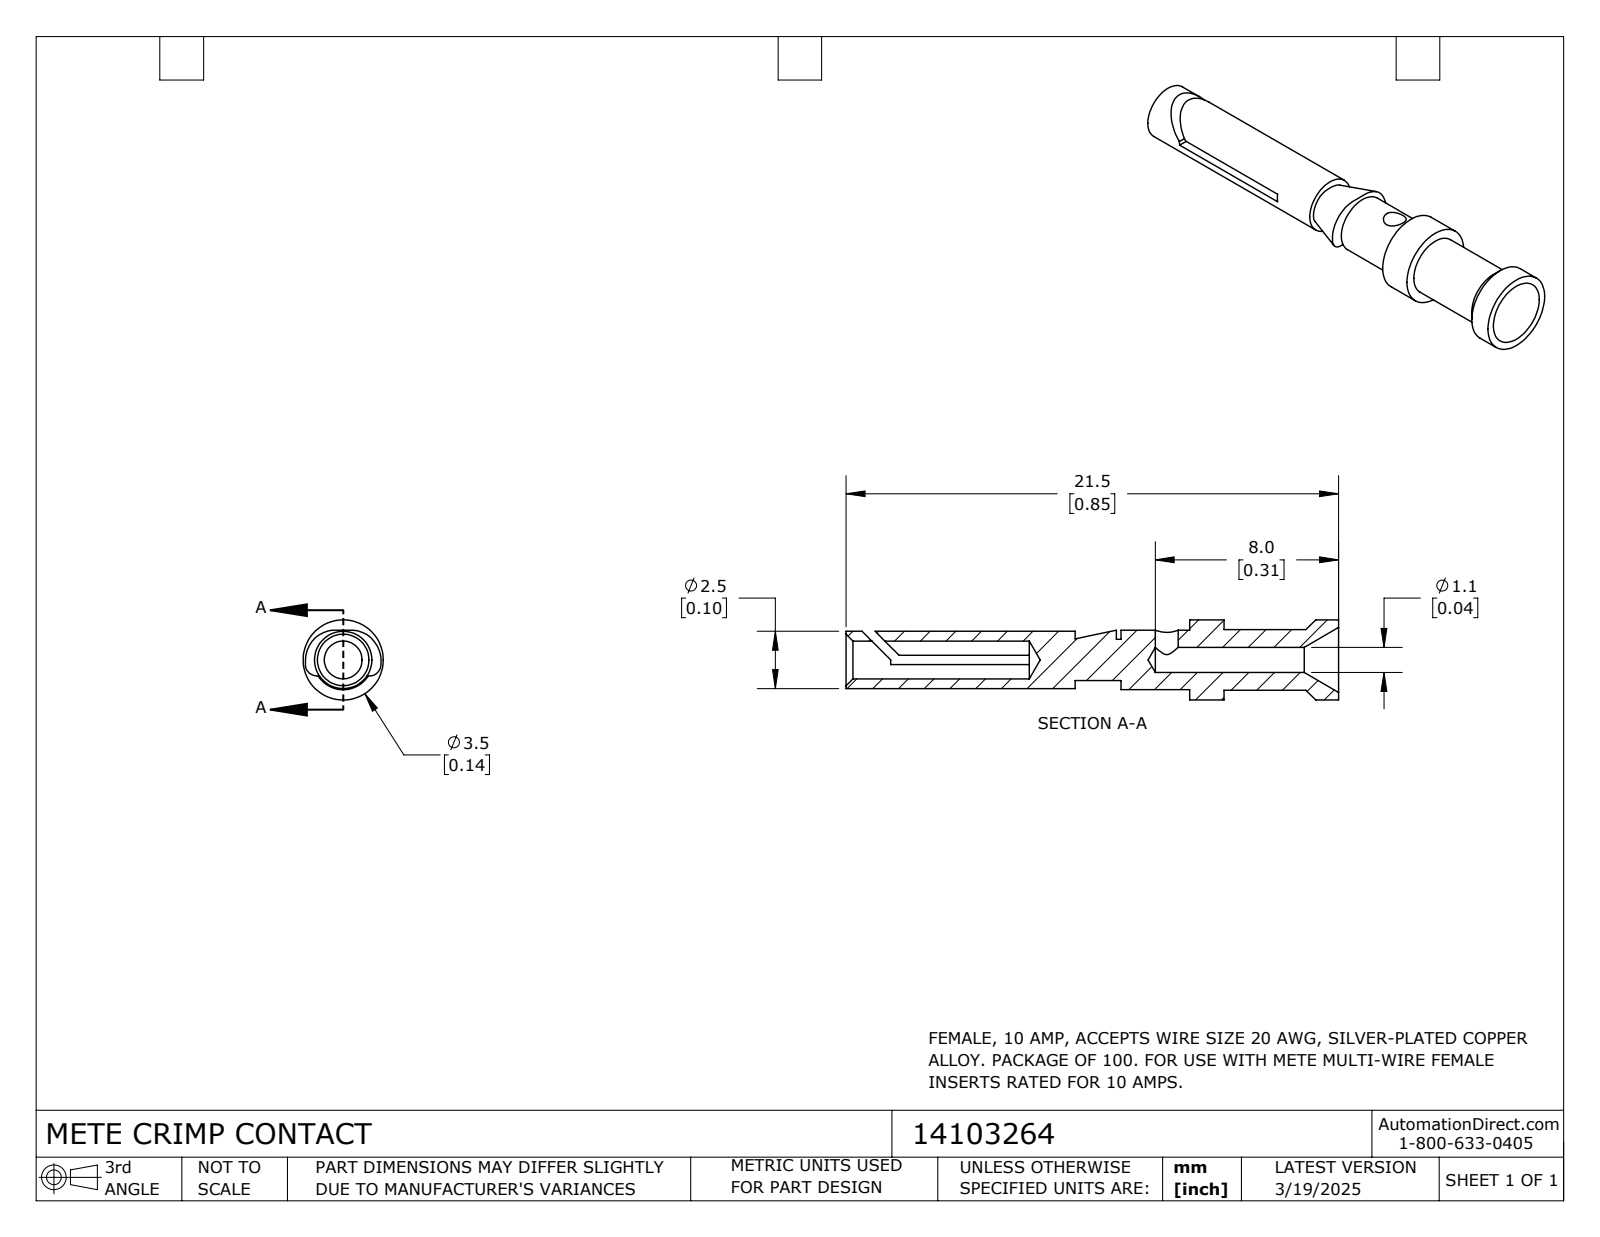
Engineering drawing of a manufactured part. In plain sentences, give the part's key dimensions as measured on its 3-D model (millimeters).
The part is named "14103264". Its 3-D file was written by "SolidWorks 2024 (CONFIG_CONTROL_DESIGN)". It is 1 solid with 48 faces: 17 planar, 20 cylindrical and 11 other. Overall it measures 21.5 by 3.5 by 3.5 millimeters. Its volume is 88 cubic millimeters and its surface area 284 square millimeters. Round holes: 1 of diameter 1, 1 of diameter 1.1, 1 of diameter 1.65. Round bosses or shafts: 1 of diameter 3.5, 1 of diameter 2.65, 1 of diameter 2.6, 1 of diameter 2.5, 1 of diameter 1.8. The main face-to-face distances are 0.4, 5, 6.5, 1.5, 4.7, 3.2, 9.7, 9.5, 4.5, 3.
